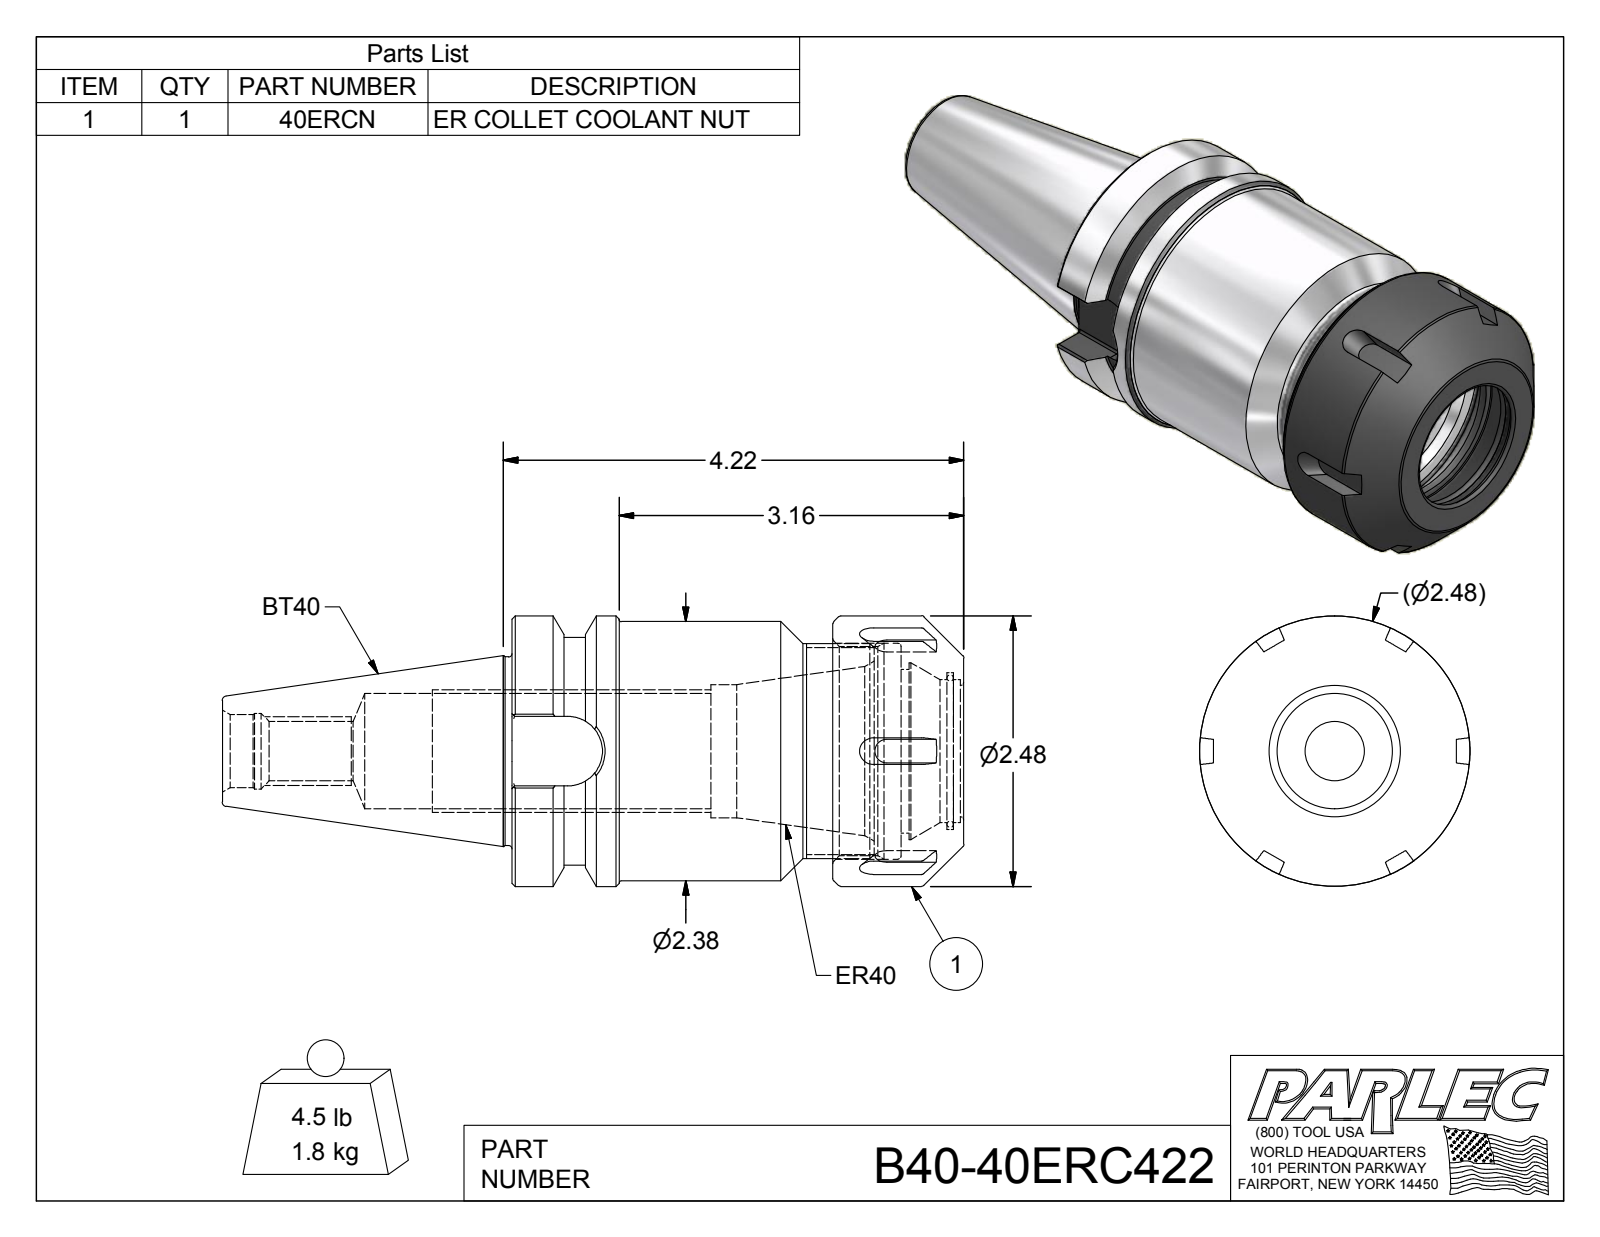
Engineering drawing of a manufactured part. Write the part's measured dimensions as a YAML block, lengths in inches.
part_name: "B40-40ERC422; B40-40ER4-1; 40ERCN"
step_written_by: "Autodesk Inventor 2012 (AUTOMOTIVE_DESIGN)"
units: inches
bodies: {solids: 2, faces: 129, planar: 50, cylindrical: 31, other: 48}
overall_size: [6.795, 2.48, 2.48]
volume: 14.52
surface_area: 84.82
round_holes:
  - {diameter: 0.545, count: 1}
  - {diameter: 0.67, count: 1}
  - {diameter: 0.694, count: 1}
  - {diameter: 1.057, count: 1}
  - {diameter: 1.22, count: 1}
  - {diameter: 1.313, count: 1}
  - {diameter: 1.437, count: 1}
  - {diameter: 1.5, count: 1}
  - {diameter: 1.62, count: 1}
  - {diameter: 1.916, count: 1}
  - {diameter: 1.98, count: 1}
round_bosses_or_shafts:
  - {diameter: 2.48, count: 1}
  - {diameter: 2.48, count: 1}
  - {diameter: 2.375, count: 1}
  - {diameter: 2.087, count: 1}
  - {diameter: 1.969, count: 1}
  - {diameter: 1.73, count: 1}
partial_cylinders:
  - {radius: 0.02, count: 8}
  - {radius: 0.319, count: 1}
face_to_face_distances: [3.567, 4.142, 0.575, 2.942, 0.625, 1.2, 3.322, 0.38, 0.245, 0.82]
